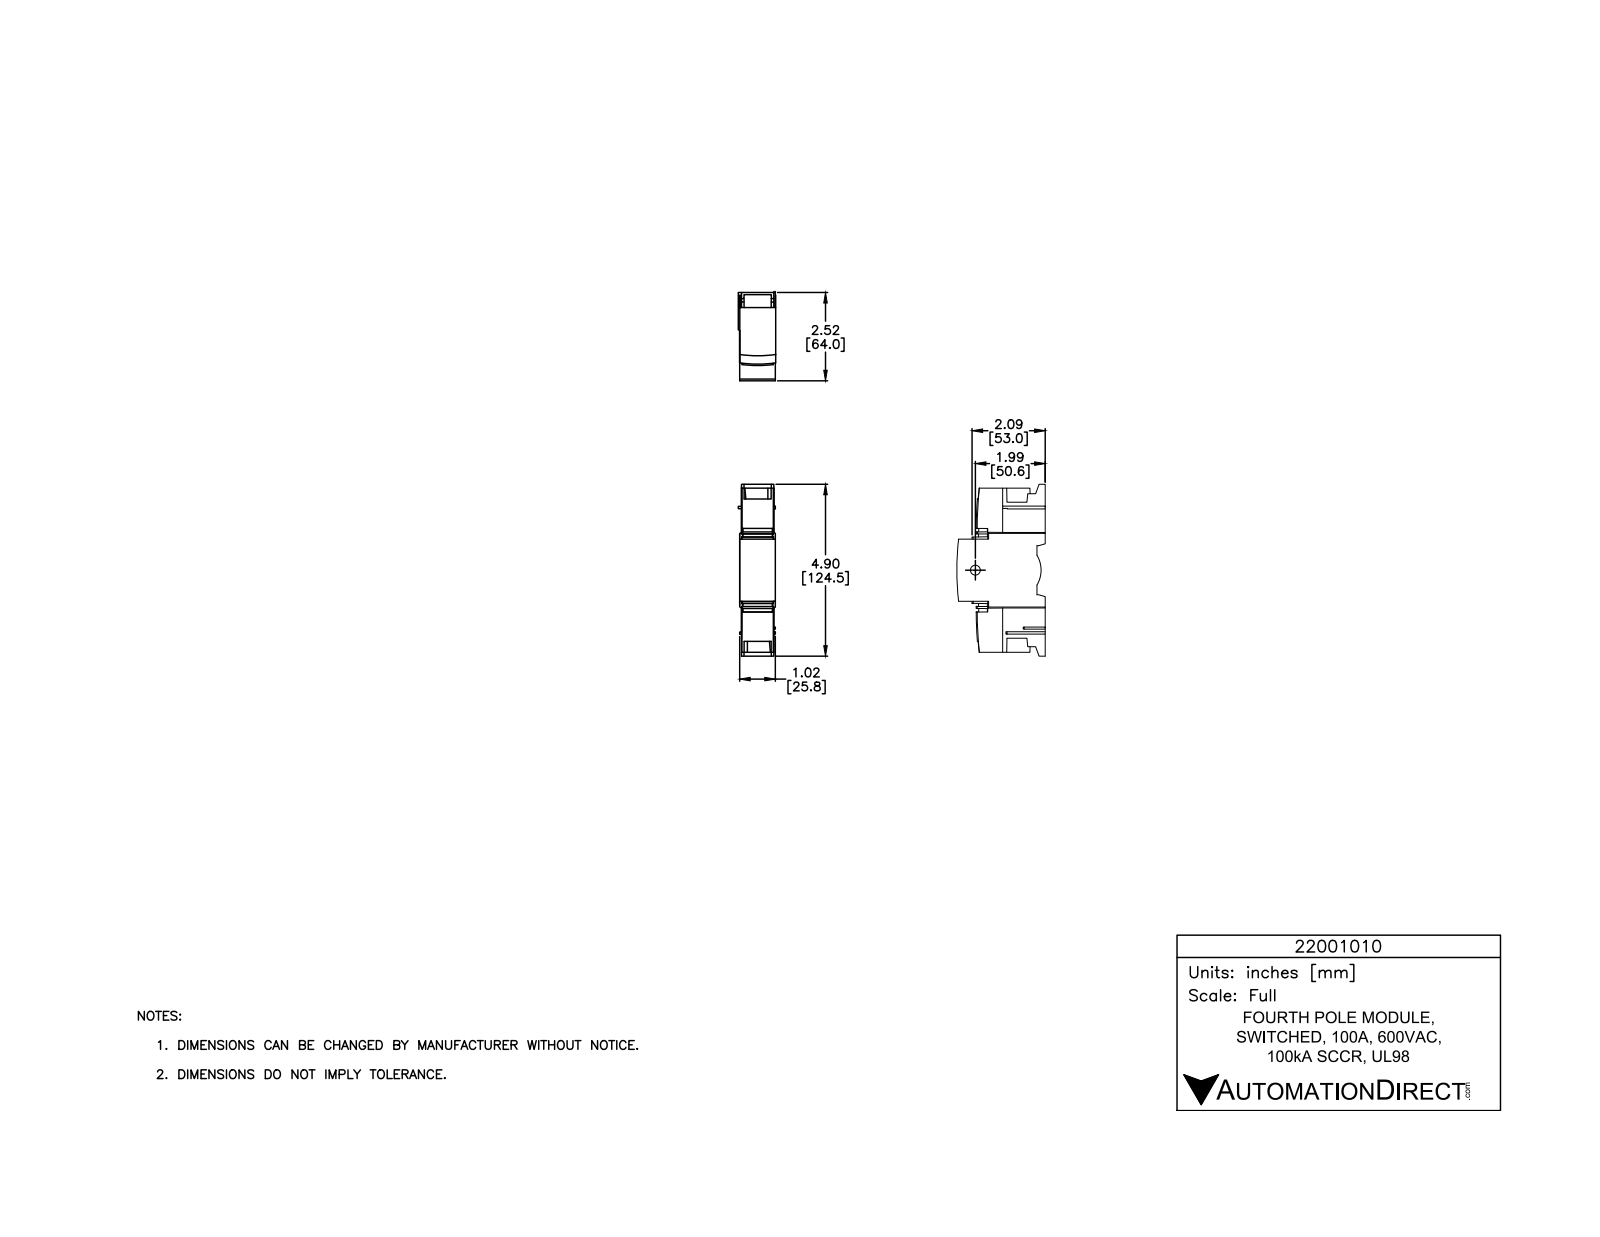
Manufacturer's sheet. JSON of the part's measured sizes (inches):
{"part_name": "22001010-UL", "step_written_by": "SolidWorks 2021 (CONFIG_CONTROL_DESIGN)", "units": "inches", "bodies": {"solids": 1, "faces": 166, "planar": 151, "cylindrical": 11, "other": 4}, "overall_size": [4.902, 2.519, 1.055], "volume_in3": 7.941, "surface_area_in2": 43.37, "round_holes": [[0.283, 1]], "partial_cylinders_radius": [[0.827, 1], [3.543, 1], [3.646, 1], [7.874, 1]], "face_to_face_distances": [1.016, 0.051, 0.965, 0.972, 0.921, 0.043, 0.553, 0.169, 0.752, 1.189]}
